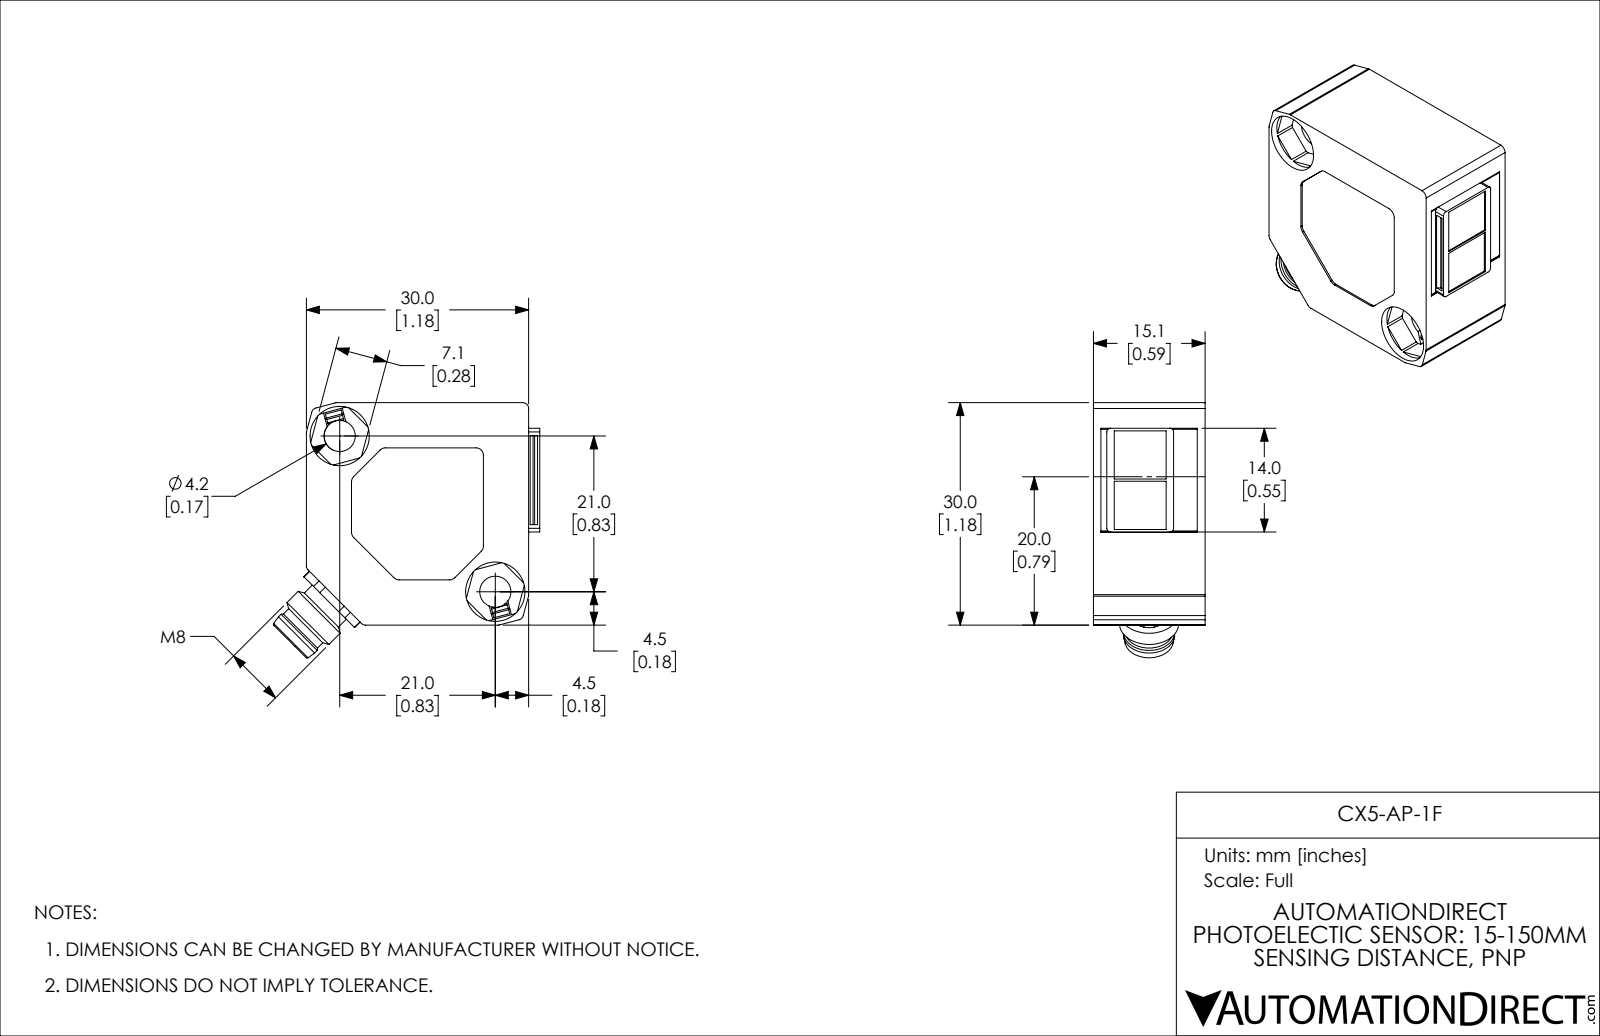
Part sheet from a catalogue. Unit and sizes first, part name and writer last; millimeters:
Units: millimetres
Overall size (bounding box): 39.45 × 34.45 × 15
Round holes (diameter × count): ⌀2.2 ×2, ⌀4.2 ×2, ⌀8 ×2, ⌀1.85 ×1, ⌀5.8 ×1, ⌀7.6 ×1
Round bosses / shafts (diameter × count): ⌀1 ×3, ⌀8 ×1, ⌀6.9 ×1, ⌀6.5 ×1
Partial cylindrical surfaces — rounded edges, fillets, slot ends (radius × count): R0.8 ×9, R1 ×7, R0.2 ×4, R0.15 ×2, R0.3 ×2, R0.46 ×2, R4.85 ×1
Main face-to-face distances: 15, 30, 14.75, 11.2, 3.8, 3.55, 7.1, 0.92, 33.75, 5
Hole centre spacings: 1.73, 4.4, 5, 5.47, 5.86, 5.96, 29.7
Volume: 12 797 mm³ · Surface area: 4 678 mm²
Bodies: 1 solid, 209 faces (123 planar, 68 cylindrical, 18 other)
Part name (STEP PRODUCT): LHS_3031_303
STEP written by: SolidWorks 2021 (AUTOMOTIVE_DESIGN)
